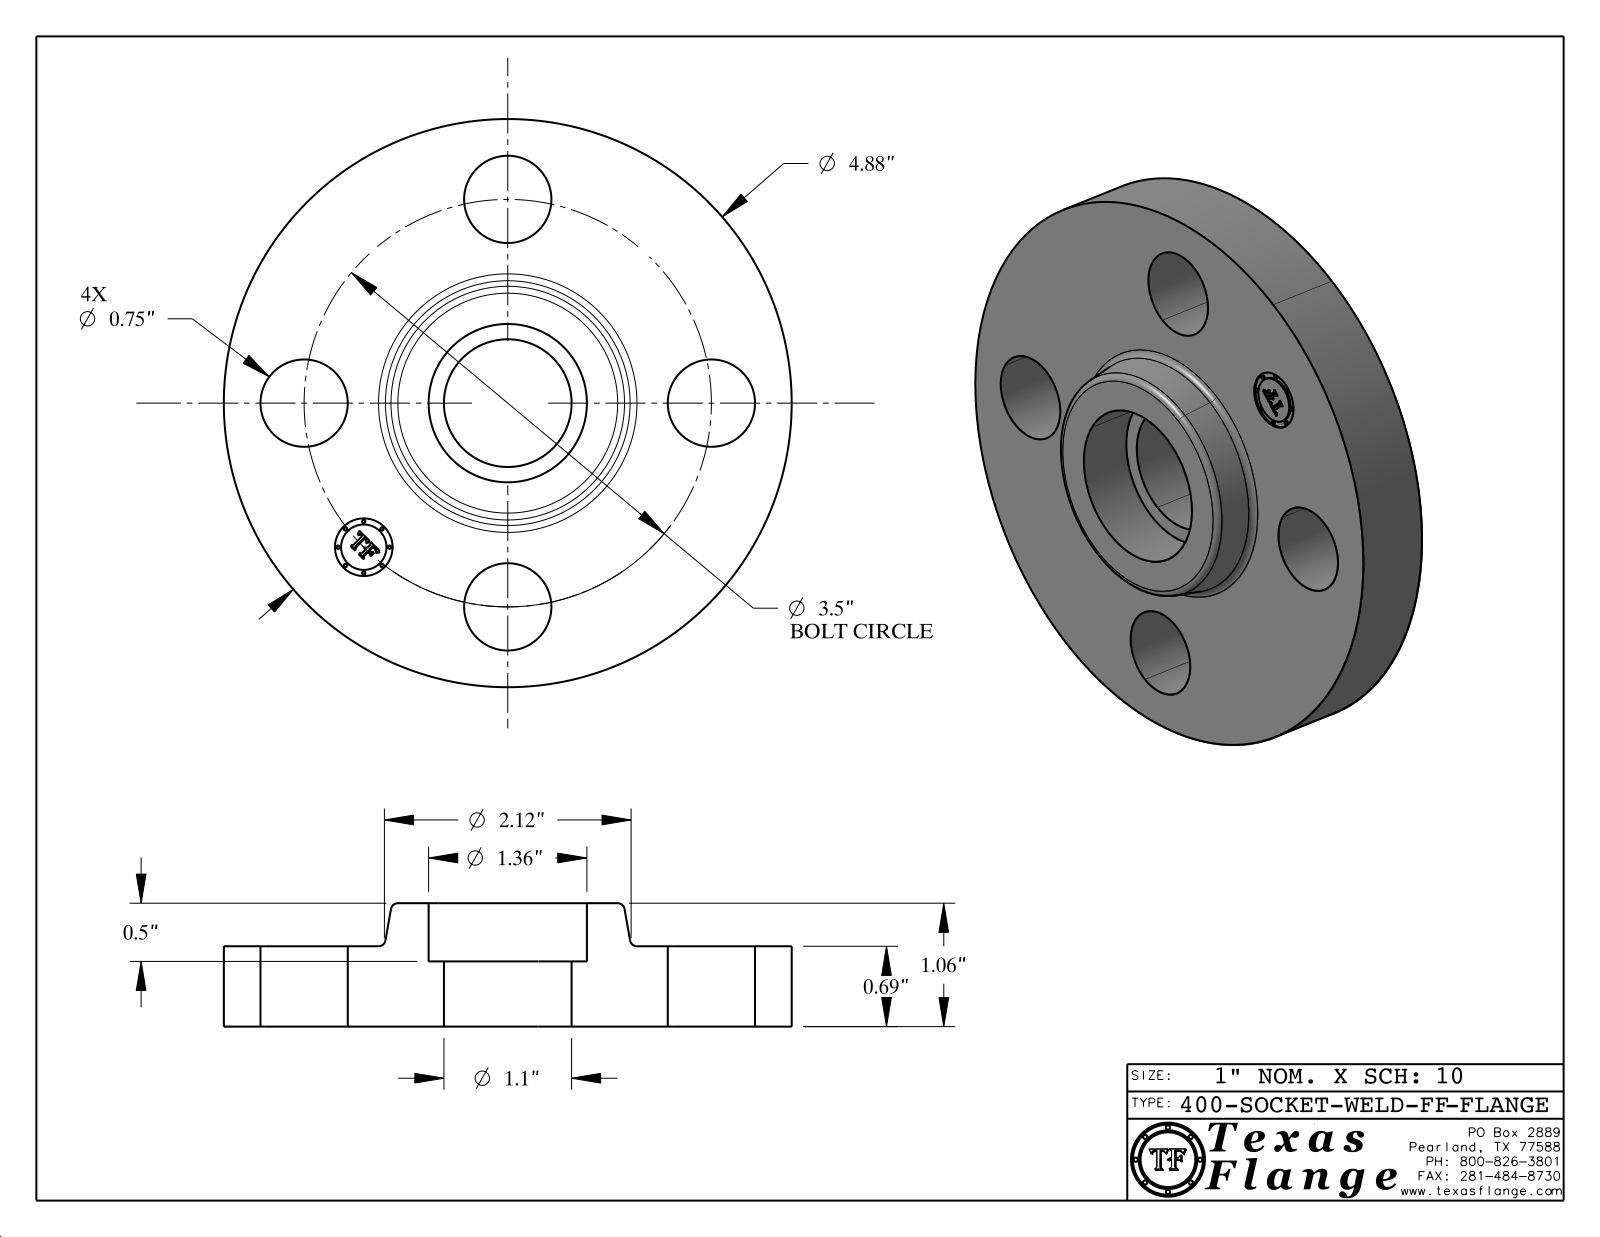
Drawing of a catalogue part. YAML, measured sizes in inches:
part_name: "400-SOCKET-WELD-FF"
step_written_by: "CATIA V5 STEP AP214 (AUTOMOTIVE_DESIGN)"
units: inches
bodies: {solids: 1, faces: 409, planar: 369, cylindrical: 34, other: 6}
overall_size: [4.88, 4.88, 1.06]
volume: 11.66
surface_area: 55.01
round_holes:
  - {diameter: 0.75, count: 4}
  - {diameter: 0.495, count: 1}
  - {diameter: 1.097, count: 1}
  - {diameter: 1.36, count: 1}
round_bosses_or_shafts:
  - {diameter: 0.03, count: 8}
  - {diameter: 4.88, count: 1}
  - {diameter: 0.39, count: 1}
face_to_face_distances: [0.69, 1.06, 0.37, 0.56, 0.13, 0.5, 0.015, 0.675, 0.115, 0.385]
hole_center_spacings: [1.75, 2.475, 1.339, 3.233, 3.5]
